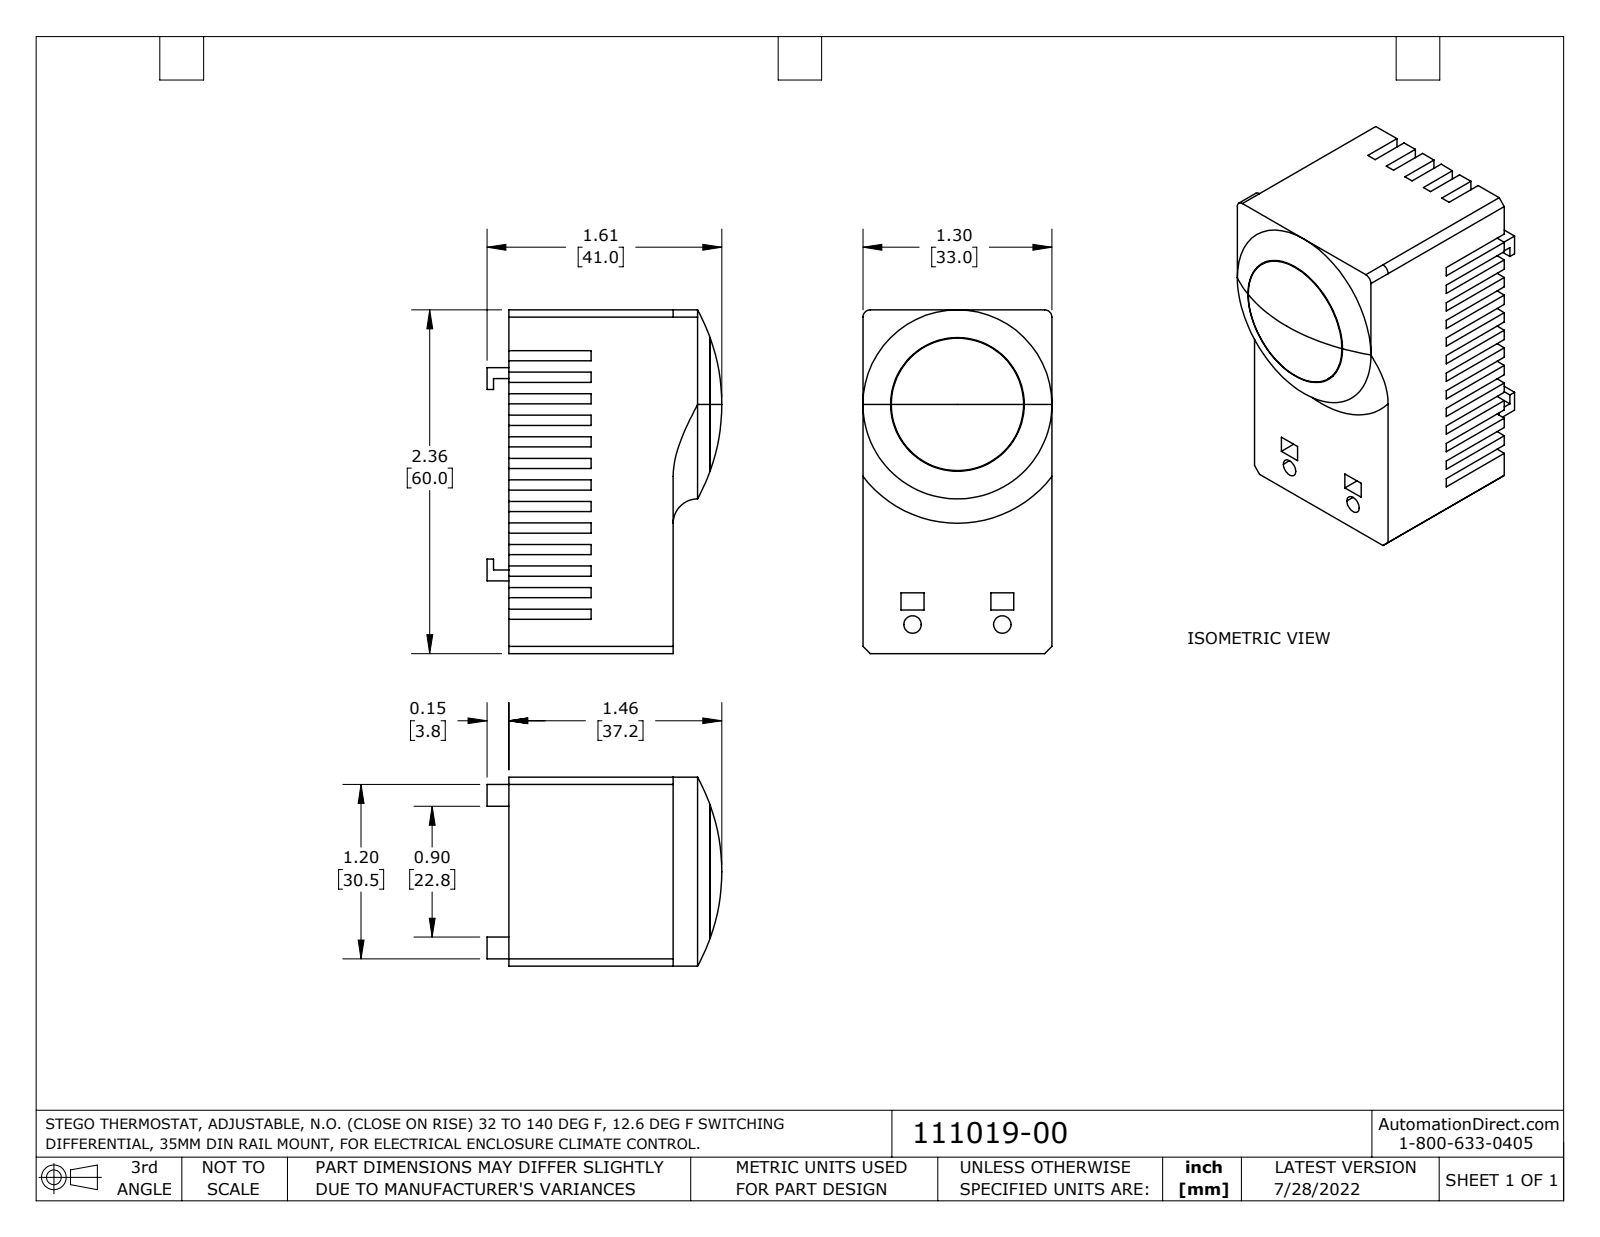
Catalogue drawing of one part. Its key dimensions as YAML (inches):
part_name: "111019-00_Default"
step_written_by: "SolidWorks 2021 (CONFIG_CONTROL_DESIGN)"
units: inches
bodies: {solids: 1, faces: 198, planar: 183, cylindrical: 10, other: 5}
overall_size: [2.362, 1.614, 1.299]
volume: 3.737
surface_area: 19.92
round_holes:
  - {diameter: 0.12, count: 2}
  - {diameter: 0.919, count: 1}
round_bosses_or_shafts:
  - {diameter: 0.909, count: 1}
partial_cylinders:
  - {radius: 0.05, count: 2}
face_to_face_distances: [1.299, 0.148, 0.07, 2.362, 0.296, 1.13, 0.444, 0.592, 0.078, 0.218]
hole_center_spacings: [1.544, 0.617]
